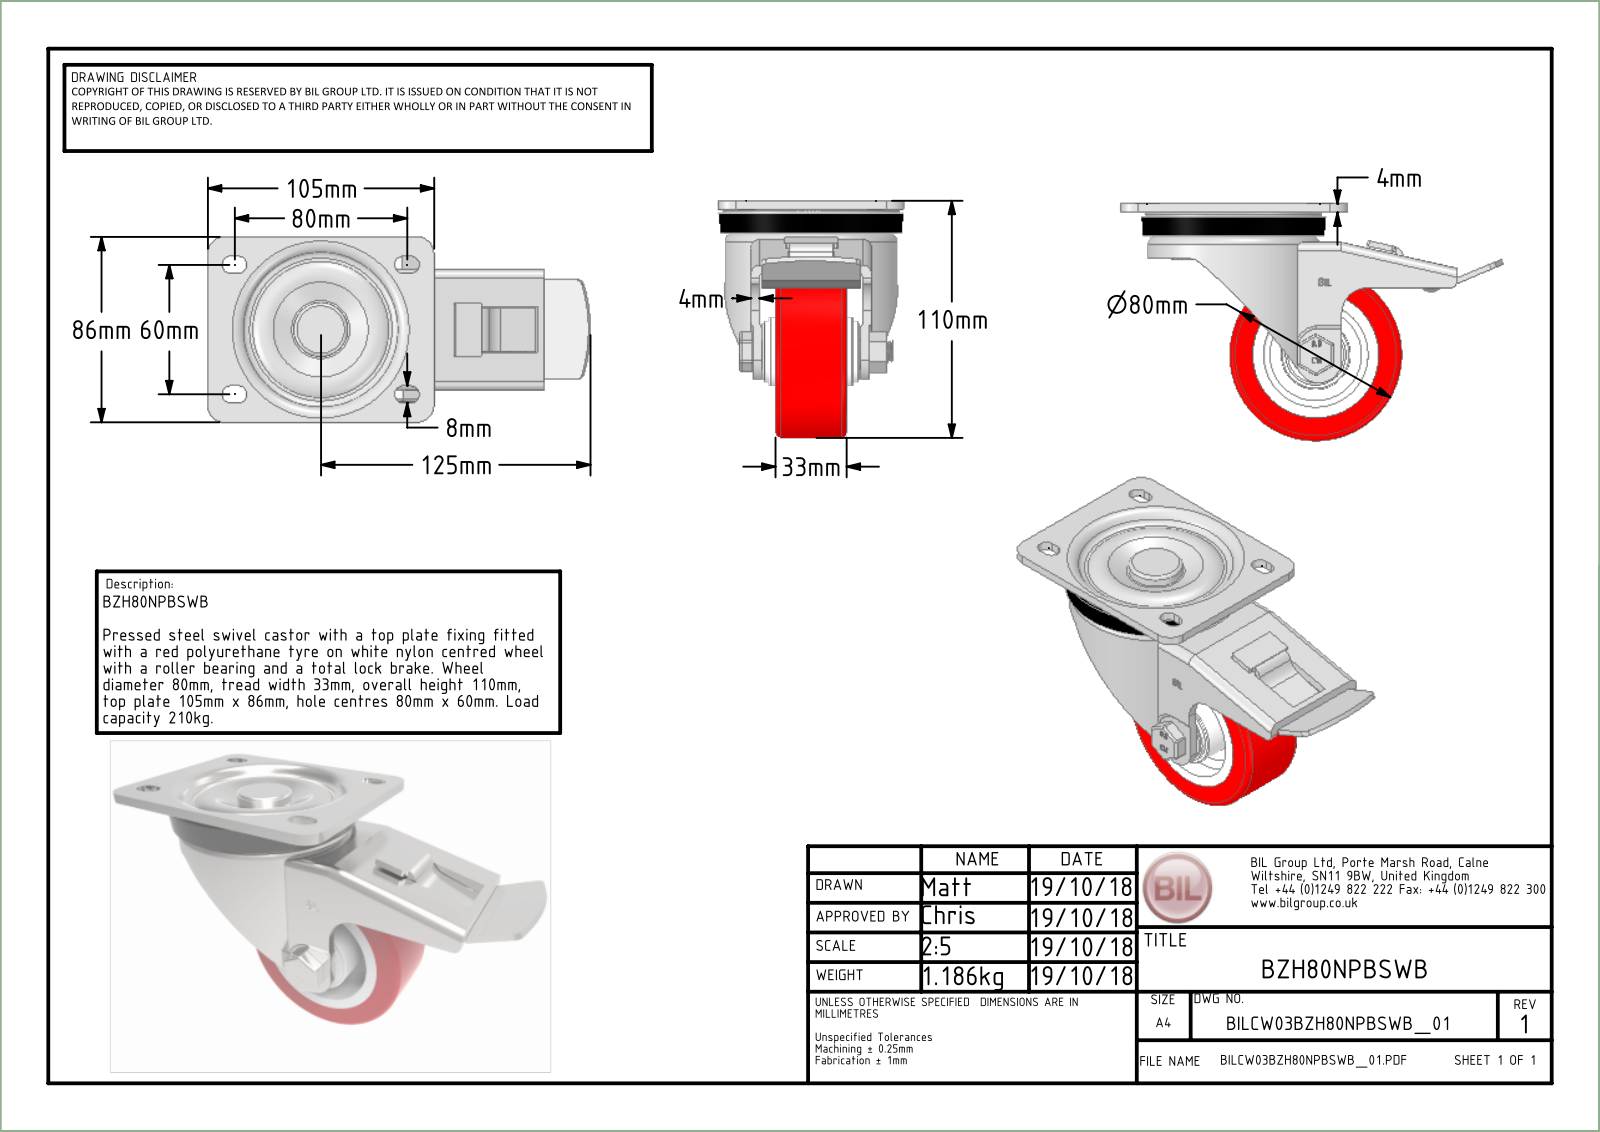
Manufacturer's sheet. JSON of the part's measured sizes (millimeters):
{"part_name": "BZH80NPBSWB v3; BZH80ASSWB v1; ZINC PLATED, PRESSED STEEL TOP PLATE; ZINC PLATED, PRESSED STEEL FORKS (+8 more)", "step_written_by": "Autodesk Translation Framework v14.10.0.0 (AUTOMOTIVE_DESIGN)", "units": "millimeters", "bodies": {"solids": 22, "faces": 682, "planar": 380, "cylindrical": 204, "other": 98}, "overall_size": [175.5, 110, 86], "volume_mm3": 291251, "surface_area_mm2": 136276, "round_holes": [[8, 1], [10, 1], [10.2, 1], [12, 1], [12.5, 1], [13, 1], [20.8, 1], [22.5, 1], [25, 1], [32, 1], [59, 1], [72, 1]], "round_bosses_or_shafts": [[3.75, 8], [80, 1], [59, 1], [31, 1], [26.25, 1], [22.3, 1], [20, 1], [19.5, 1]], "partial_cylinders_radius": [[0.5, 18], [0.75, 12], [2, 10], [4.5, 8], [4, 5], [2.5, 4], [3, 4], [8, 4]], "face_to_face_distances": [4, 7.5, 10.5, 6.5, 1, 3.5, 11.5, 3, 0.5, 7]}
